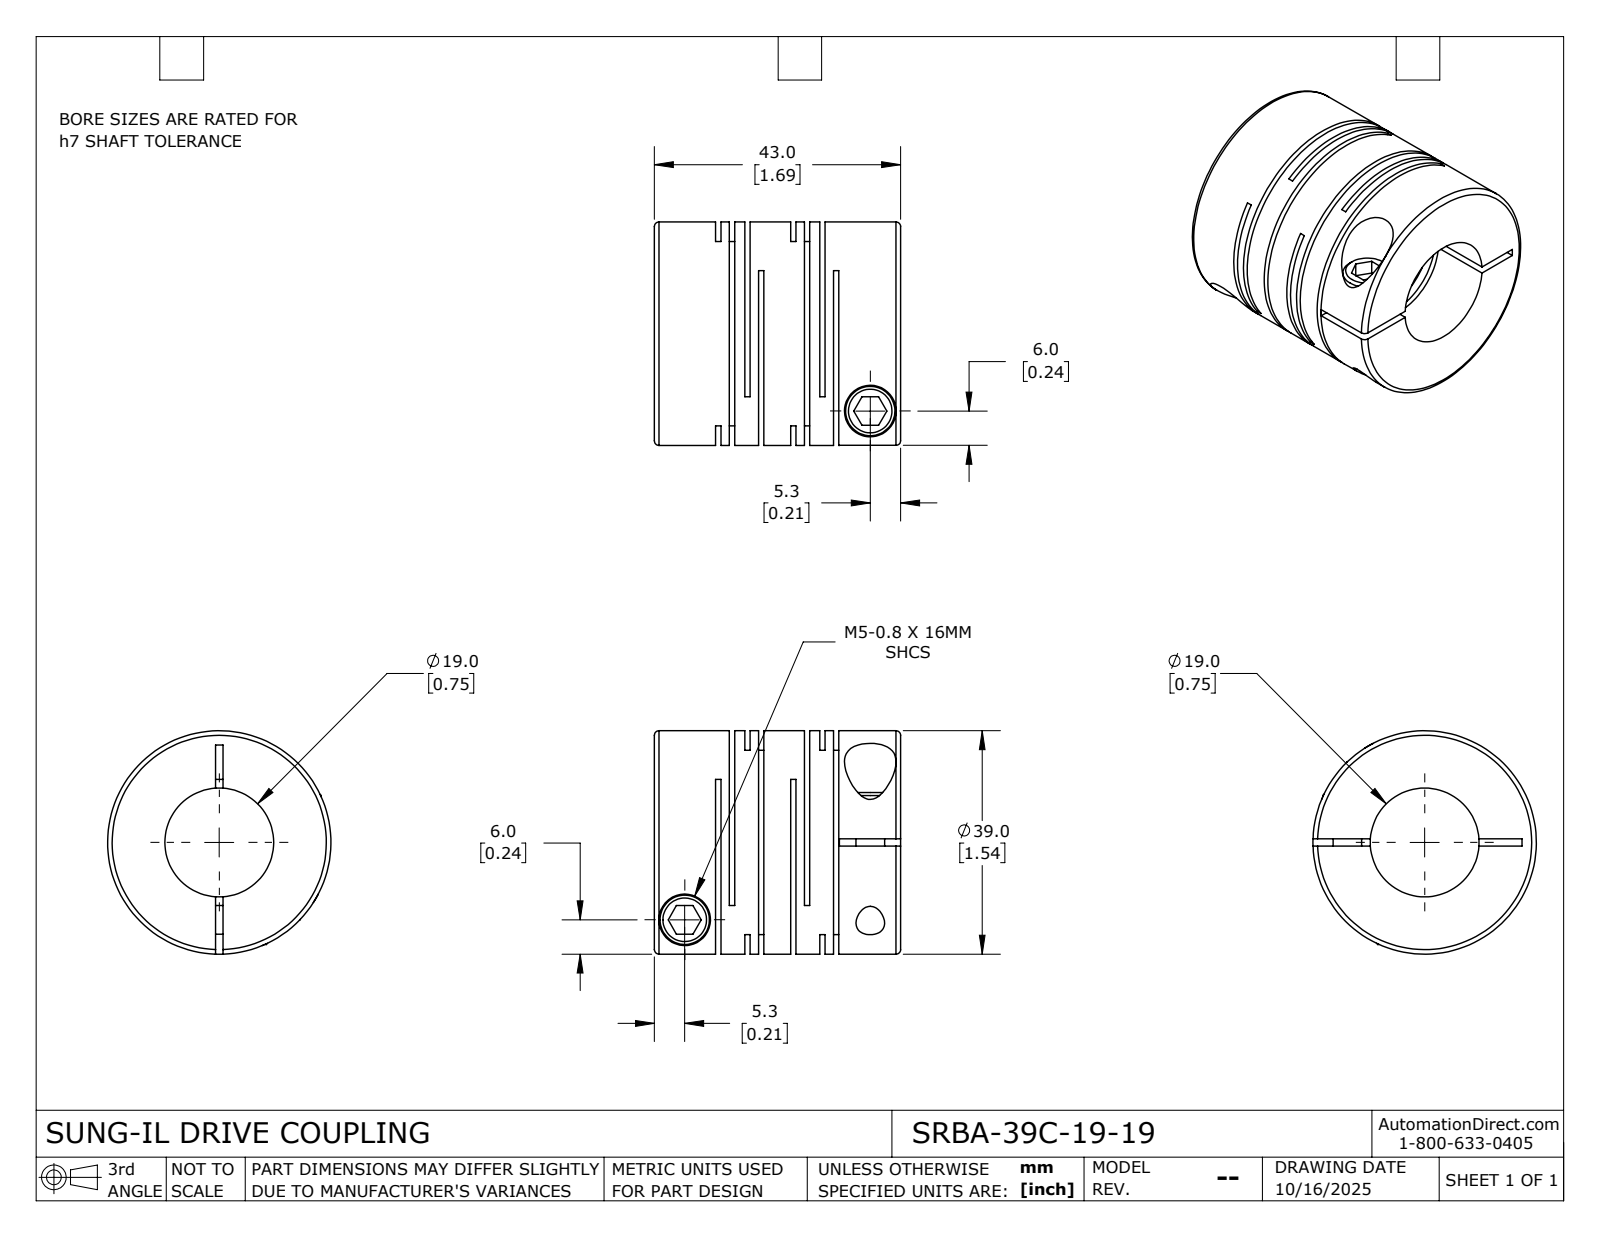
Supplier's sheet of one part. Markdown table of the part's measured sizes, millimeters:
| quantity | value |
| --- | --- |
| part name | SRBA-39C-19-19 |
| STEP written by | SolidWorks 2024 (CONFIG_CONTROL_DESIGN) |
| units | millimeters |
| bodies | 1 solid, 115 faces (60 planar, 42 cylindrical, 13 other) |
| overall size | 43 × 39 × 39 |
| volume | 32 507 mm³ |
| surface area | 21 677 mm² |
| round holes (diameter × count) | 5 × 2, 9 × 2, 19 × 1 |
| round bosses / shafts (diameter × count) | 8.6 × 2, 39 × 1 |
| main face-to-face distances | 13.1, 0.92, 2.4, 5.1, 10.7, 14.02, 18.2, 12.18, 1.48, 4.18 |
